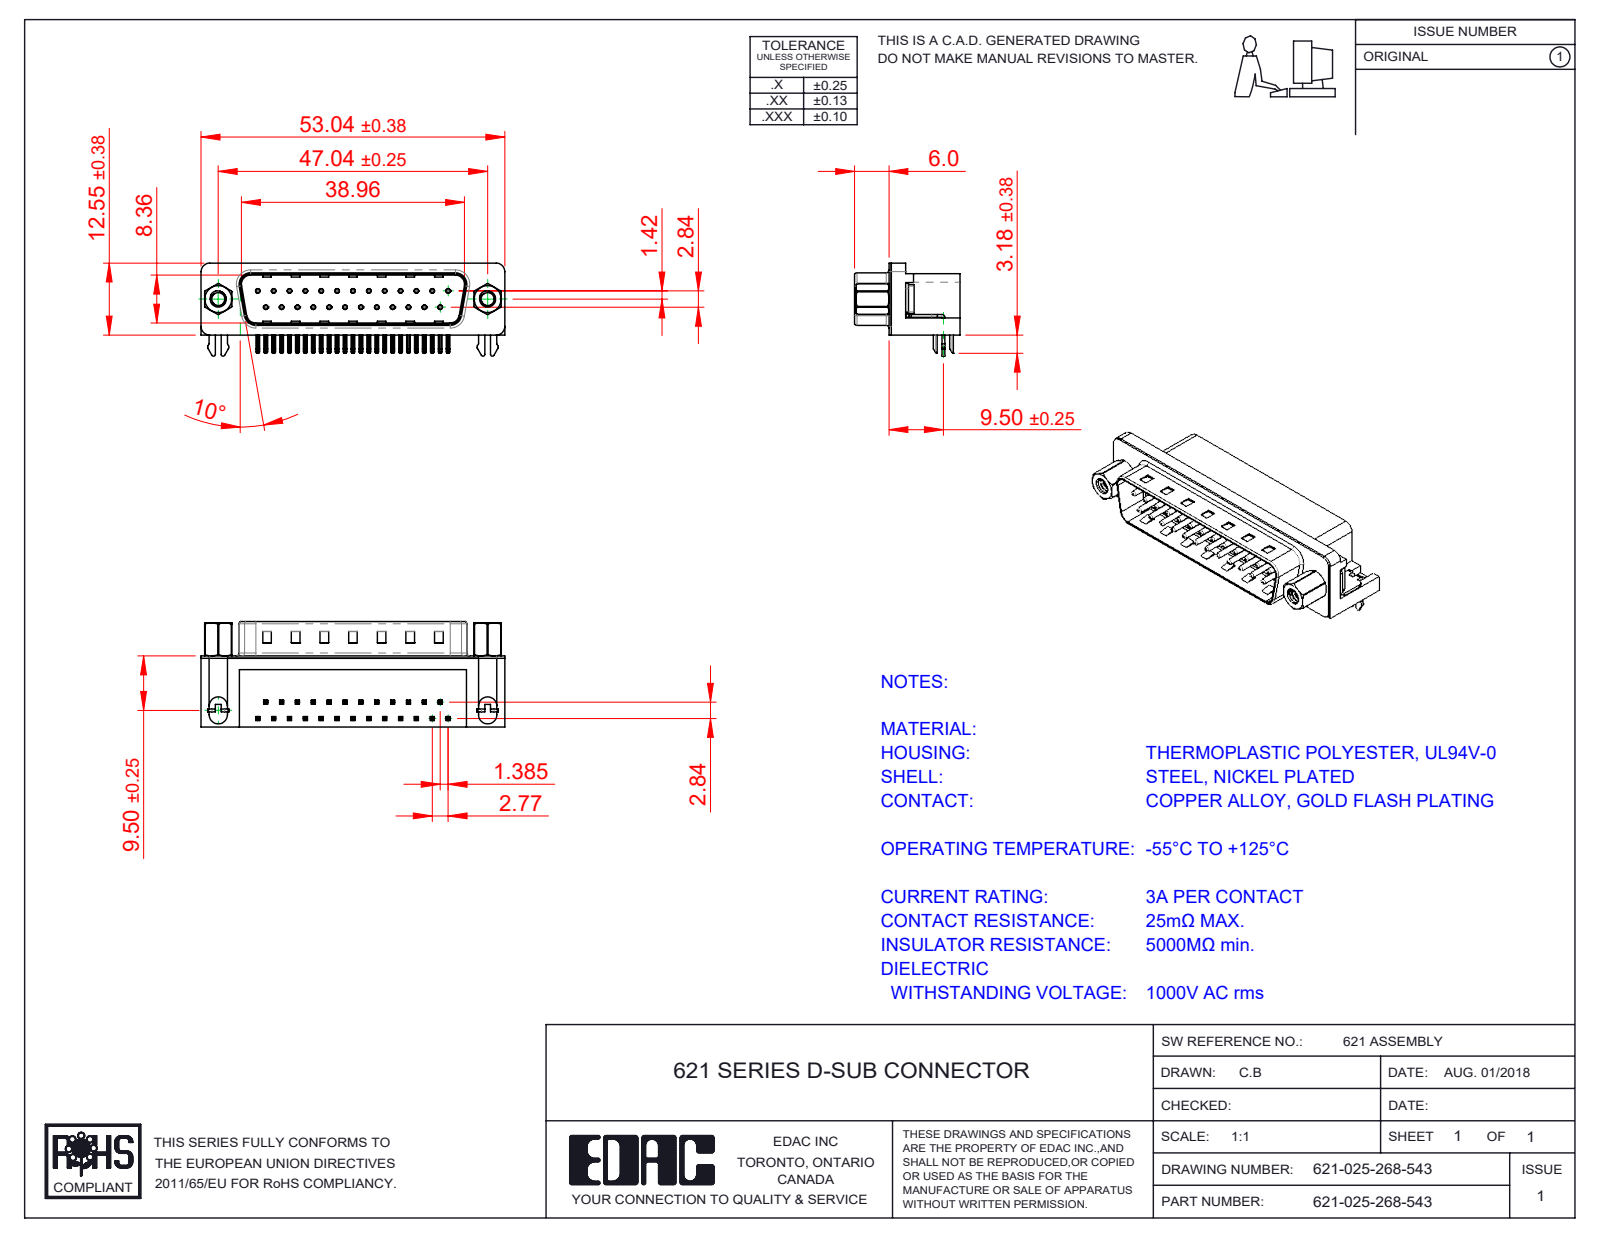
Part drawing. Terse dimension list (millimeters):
name: 621 Shell_25 Socket; 621 4-40 Hex Standoff 5; 621 4 Prong Board Lock; 621 Contact Bottom (+4 more)
written by: SolidWorks 2016 (CONFIG_CONTROL_DESIGN)
unit: mm
bodies: 33 solids, 2509 faces (1469 planar, 737 cylindrical, 303 other)
size: 53.04 × 18.4 × 16.25
volume: 6 570 mm³; area: 8 240 mm²
holes: 25× ⌀0.35, 25× ⌀0.8, 2× ⌀2, 2× ⌀2.26, 2× ⌀2.29, 2× ⌀4, 2× ⌀4.8, 2× ⌀5
bosses: 25× ⌀0.75, 2× ⌀4.9, 2× ⌀4.75, 2× ⌀3.9, 2× ⌀3, 2× ⌀2.79
rounds: 112× R0.25, 50× R0.12, 16× R1, 9× R0.5, 8× R1.6, 7× R1.5, 4× R0.9, 4× R2
face distances: 0.4, 12, 10.35, 2.1, 8.76, 10.46, 1.7, 10.86, 12.4, 9
hole spacings: 3.16, 2.77, 5.54, 8.31, 11.08, 13.85, 16.62, 5.03
